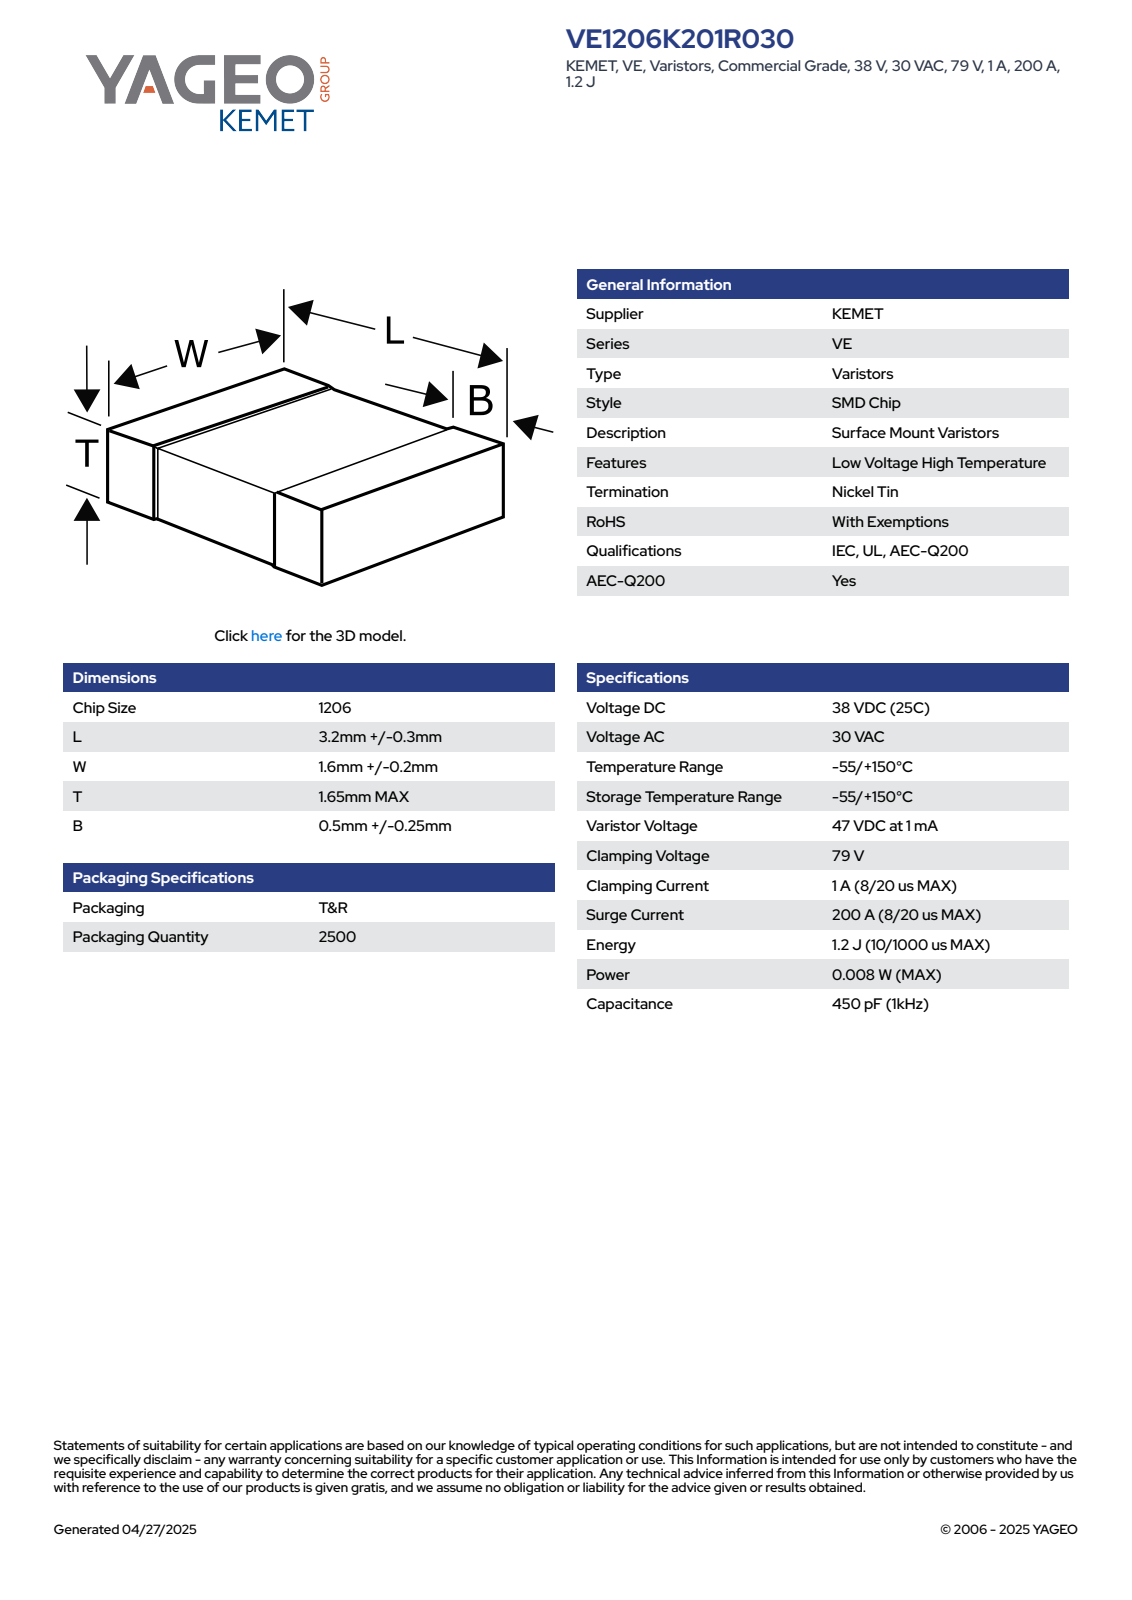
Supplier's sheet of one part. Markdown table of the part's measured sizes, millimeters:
| quantity | value |
| --- | --- |
| part name | VS_SMD_1206_L3.50W1.8T1.25B0.75 |
| STEP written by | SolidWorks 2014 (AUTOMOTIVE_DESIGN) |
| units | millimeters |
| bodies | 4 solids, 125 faces (71 planar, 38 cylindrical, 16 other) |
| overall size | 3.5 × 1.8 × 1.25 |
| volume | 7 mm³ |
| surface area | 26 mm² |
| main face-to-face distances | 1.21, 1.17, 1.76, 1.25, 1.72, 3.5, 1.8, 1.22, 1.18, 1.63 |
